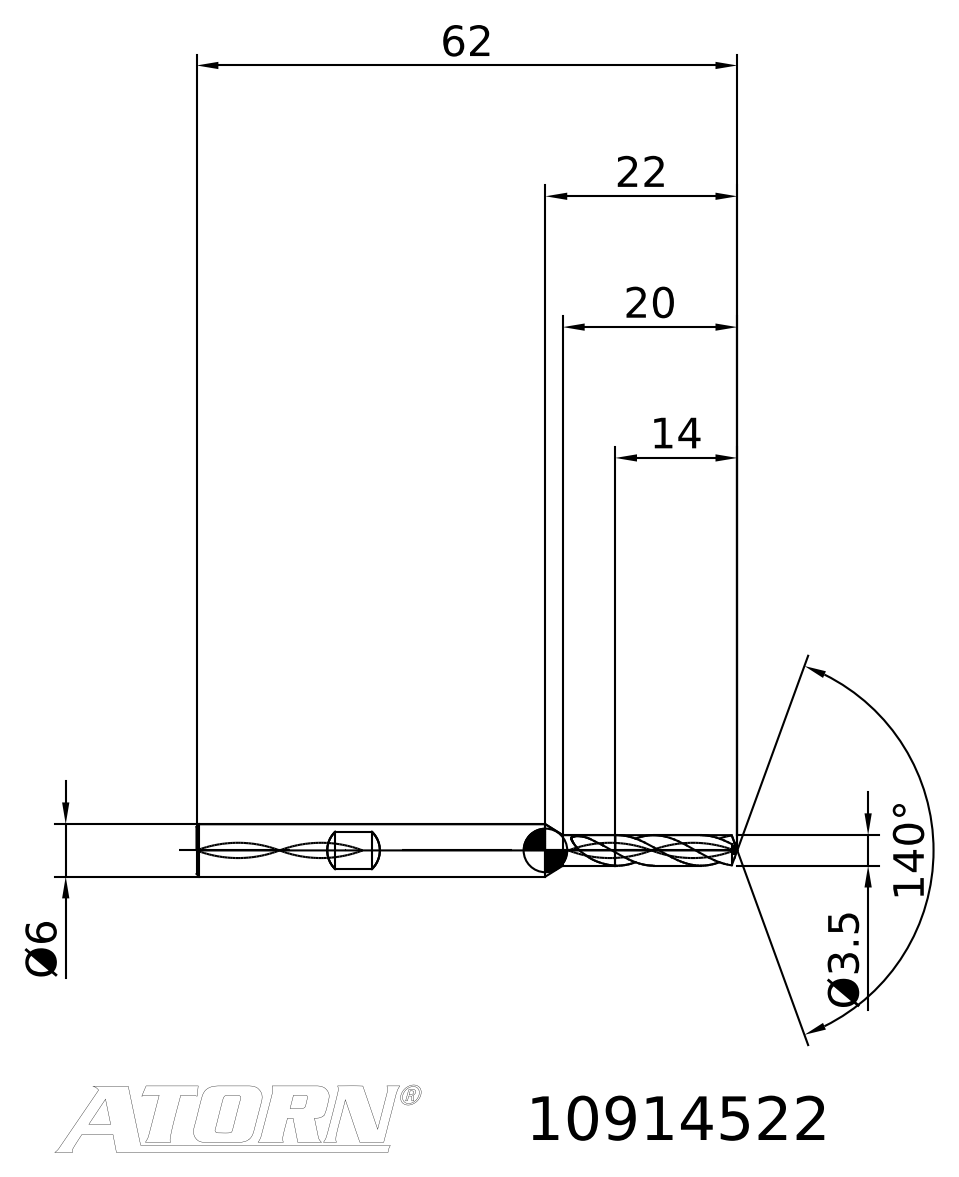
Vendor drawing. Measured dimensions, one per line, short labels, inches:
written by: TDM (AUTOMOTIVE_DESIGN)
unit: in
bodies: 2 solids, 33 faces (8 planar, 0 cylindrical, 25 other)
size: 2.441 × 0.236 × 0.236
volume: 0.078 in³; area: 1.652 in²
face distances: 1.89, 0.532, 2.422
